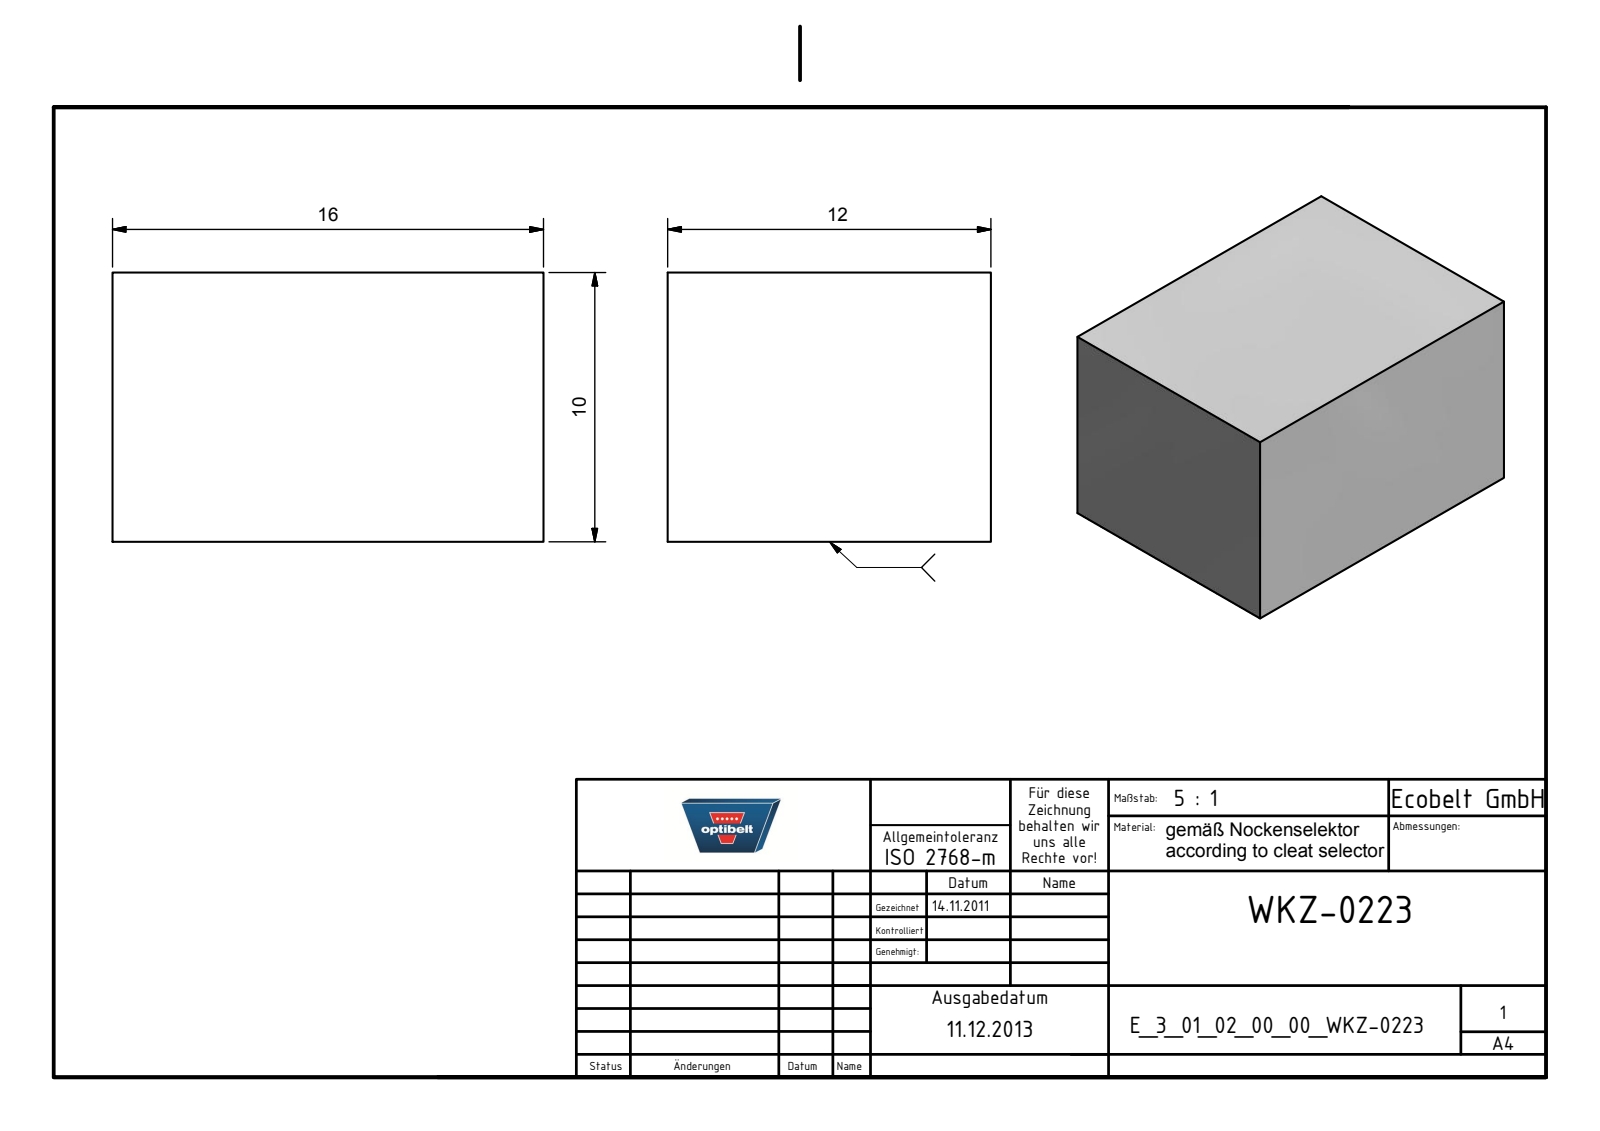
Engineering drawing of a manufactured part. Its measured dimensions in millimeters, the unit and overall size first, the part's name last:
Units: millimetres
Overall size (bounding box): 16 × 12 × 10
Main face-to-face distances: 10, 12, 16
Volume: 1 920 mm³ · Surface area: 944 mm²
Bodies: 1 solid, 6 faces (6 planar, 0 cylindrical, 0 other)
Part name (STEP PRODUCT): E_3_01_02_00_00_WKZ-0223
STEP written by: Autodesk Inventor 2021 (AUTOMOTIVE_DESIGN)
